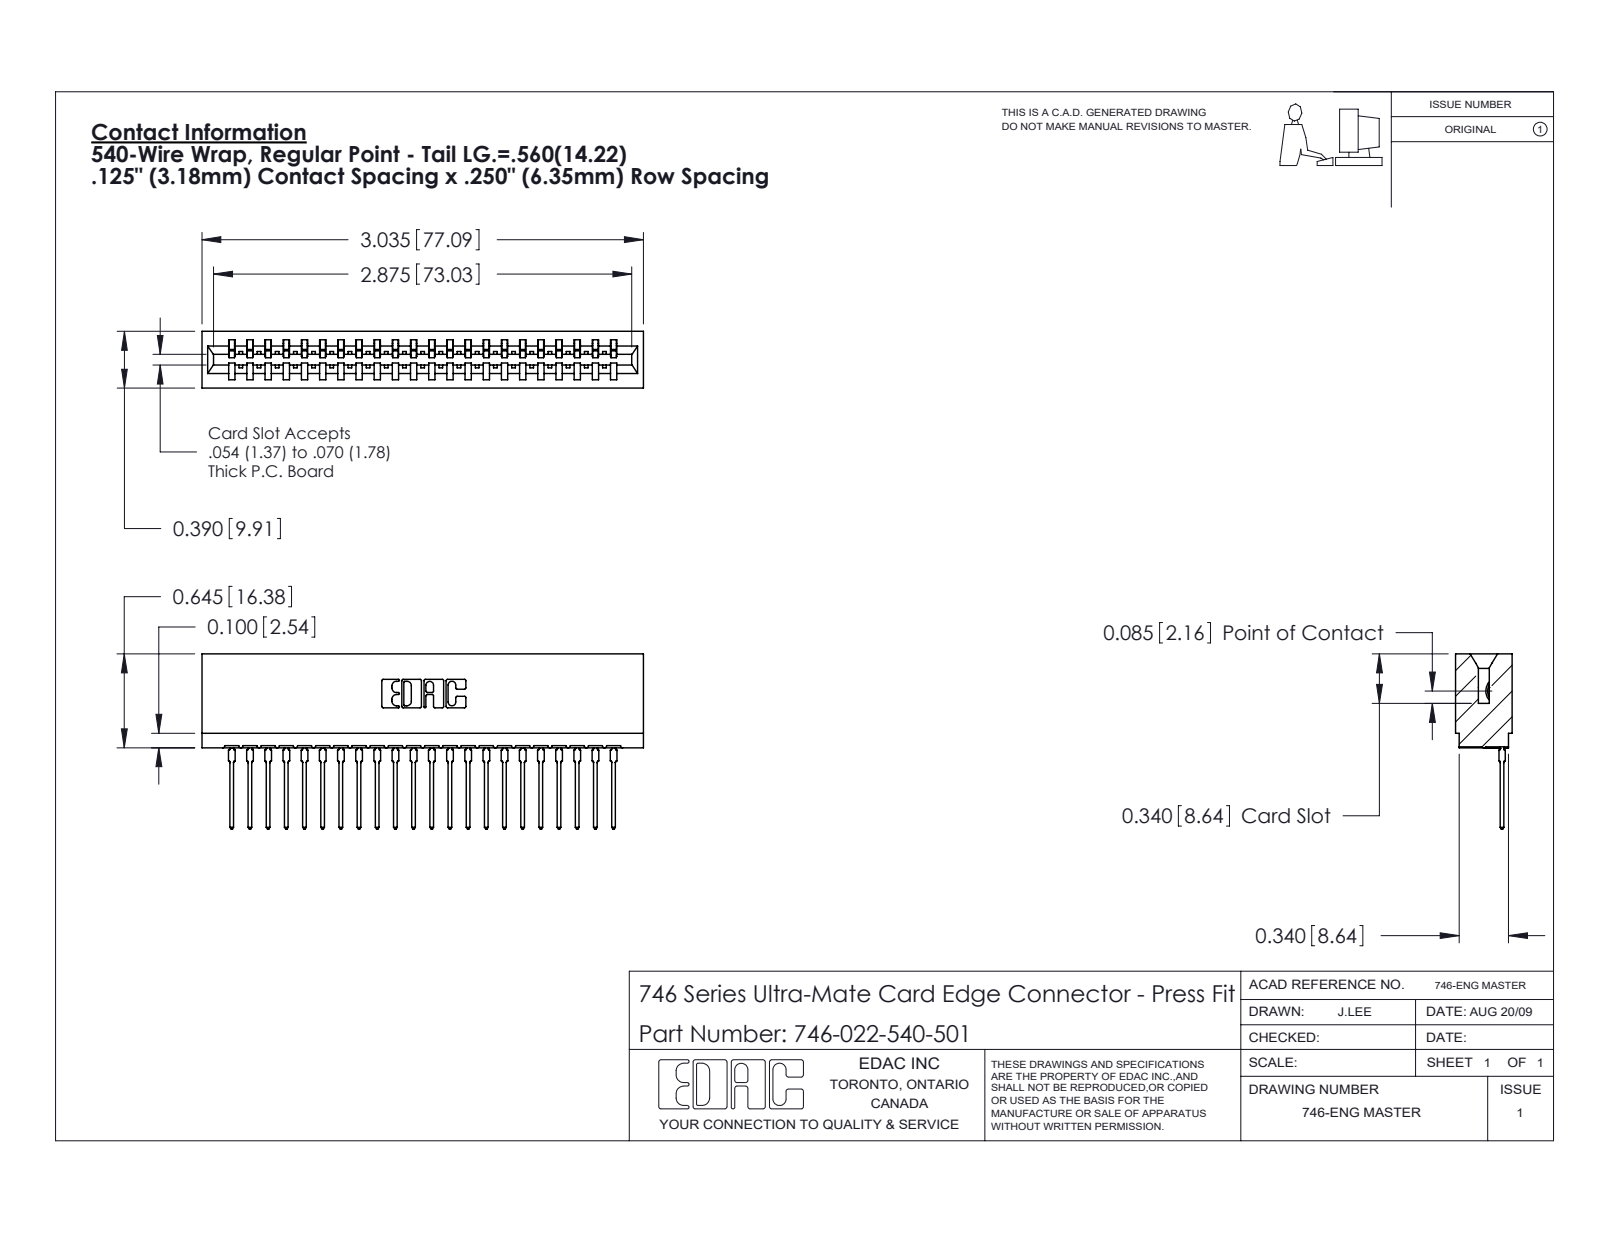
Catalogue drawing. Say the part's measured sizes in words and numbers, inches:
The part is named "746-022-540-501; 746-292-001_540; 746 Part_.340 Slot Depth - 01". Its 3-D file was written by "SolidWorks 2020 (CONFIG_CONTROL_DESIGN)". It is 23 solids with 2473 faces: 1441 planar, 460 cylindrical and 572 other. Overall it measures 3.035 by 1.204 by 0.39 inches. Its volume is 0.539 cubic inches and its surface area 18.4 square inches. Partial cylindrical surfaces (rounded edges, fillets, slot ends): 44 of radius 0.021, 23 of radius 0.015, 22 of radius 0.01, 6 of radius 0.007, 6 of radius 0.031, 4 of radius 0.005, 4 of radius 0.011, 3 of radius 0.026. The main face-to-face distances are 0.057, 0.25, 0.333, 0.39, 0.025, 0.307, 0.125, 0.375, 0.125, 0.5.
